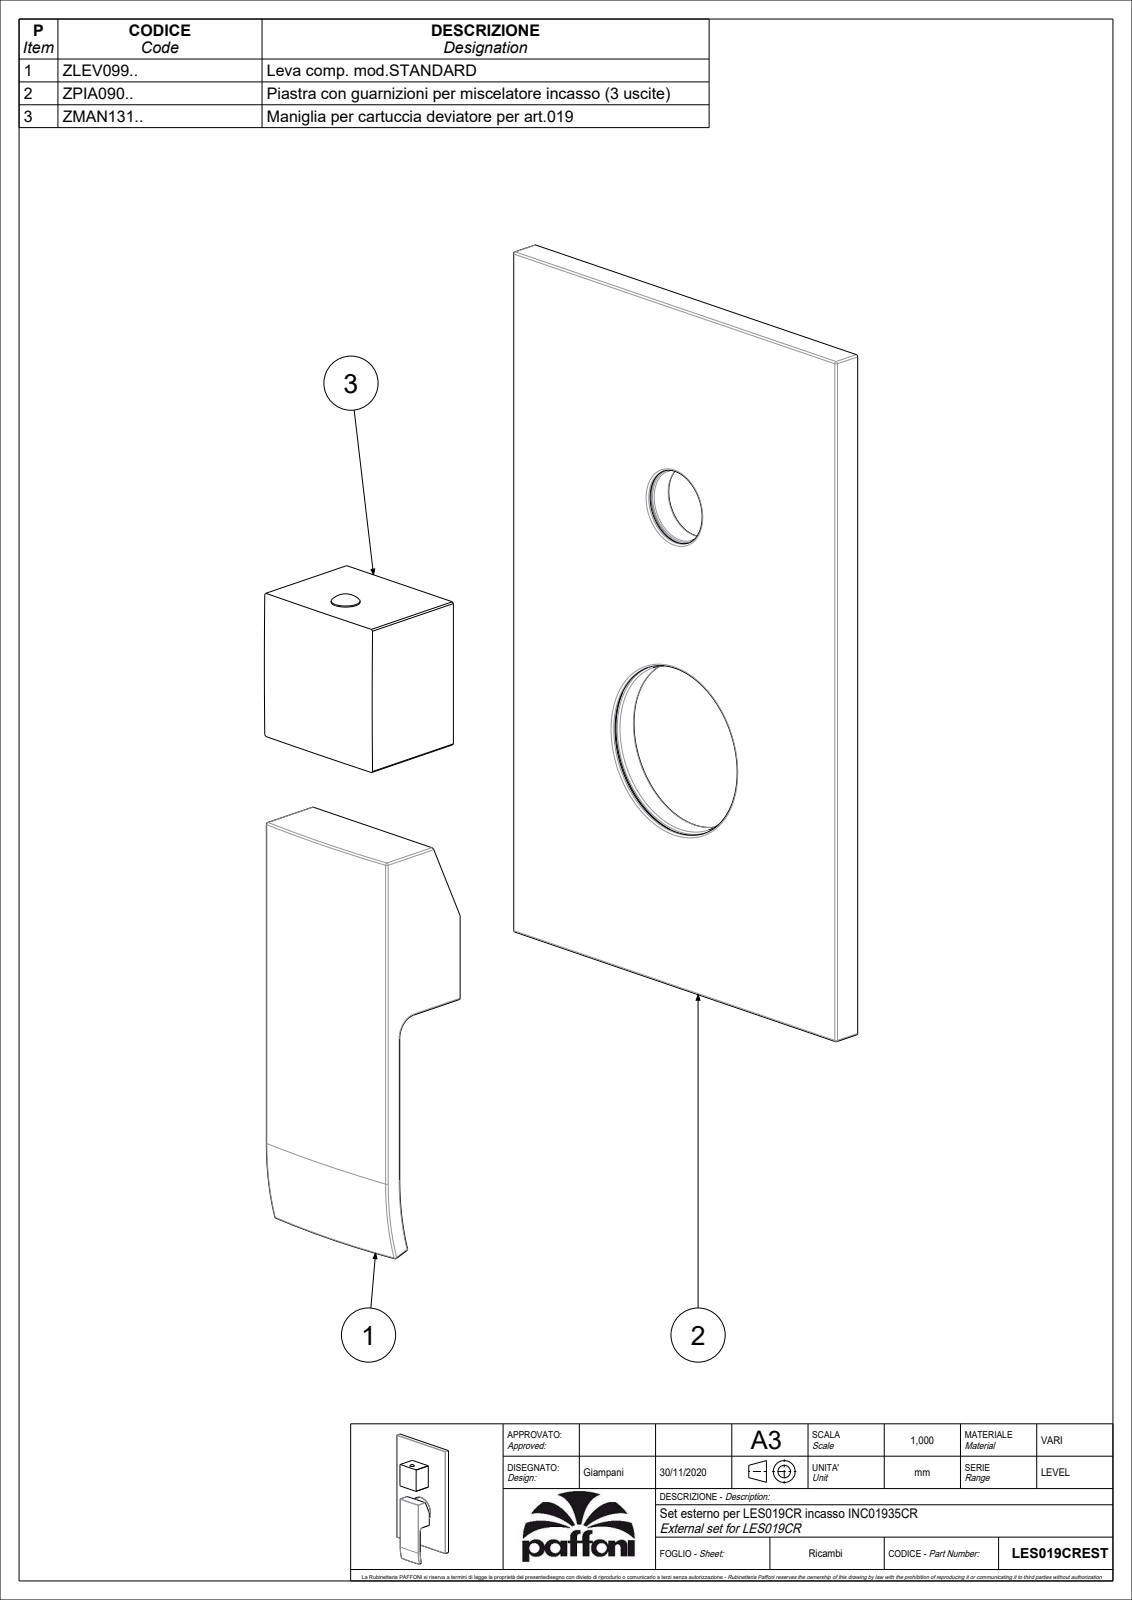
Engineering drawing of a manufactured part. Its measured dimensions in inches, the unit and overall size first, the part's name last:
Units: inches
Overall size (bounding box): 8.361 × 4.724 × 1.594
Round holes (diameter × count): ⌀0.118 ×2, ⌀0.217 ×2, ⌀0.126 ×1, ⌀0.13 ×1, ⌀0.165 ×1, ⌀0.307 ×1, ⌀0.583 ×1, ⌀0.756 ×1, ⌀0.787 ×1, ⌀0.827 ×1, ⌀0.913 ×1, ⌀1.417 ×1
Round bosses / shafts (diameter × count): ⌀0.299 ×2, ⌀0.197 ×2, ⌀2.008 ×1, ⌀1.929 ×1, ⌀0.984 ×1, ⌀0.906 ×1
Partial cylindrical surfaces — rounded edges, fillets, slot ends (radius × count): R0.02 ×18, R0.059 ×14, R0.039 ×8, R0.079 ×4, R11.811 ×2, R0.089 ×1, R1.102 ×1
Main face-to-face distances: 0.098, 0.315, 0.217, 0.02, 0.197, 0.118, 1.575, 1.476, 3.248, 3.15
Hole centre spacings: 0.276, 0.394, 2.283, 2.677
Volume: 10.65 in³ · Surface area: 170.1 in²
Bodies: 3 solids, 315 faces (109 planar, 123 cylindrical, 83 other)
Part name (STEP PRODUCT): LES018CREST
STEP written by: CREO PARAMETRIC BY PTC INC, 2020044 (CONFIG_CONTROL_DESIGN)
